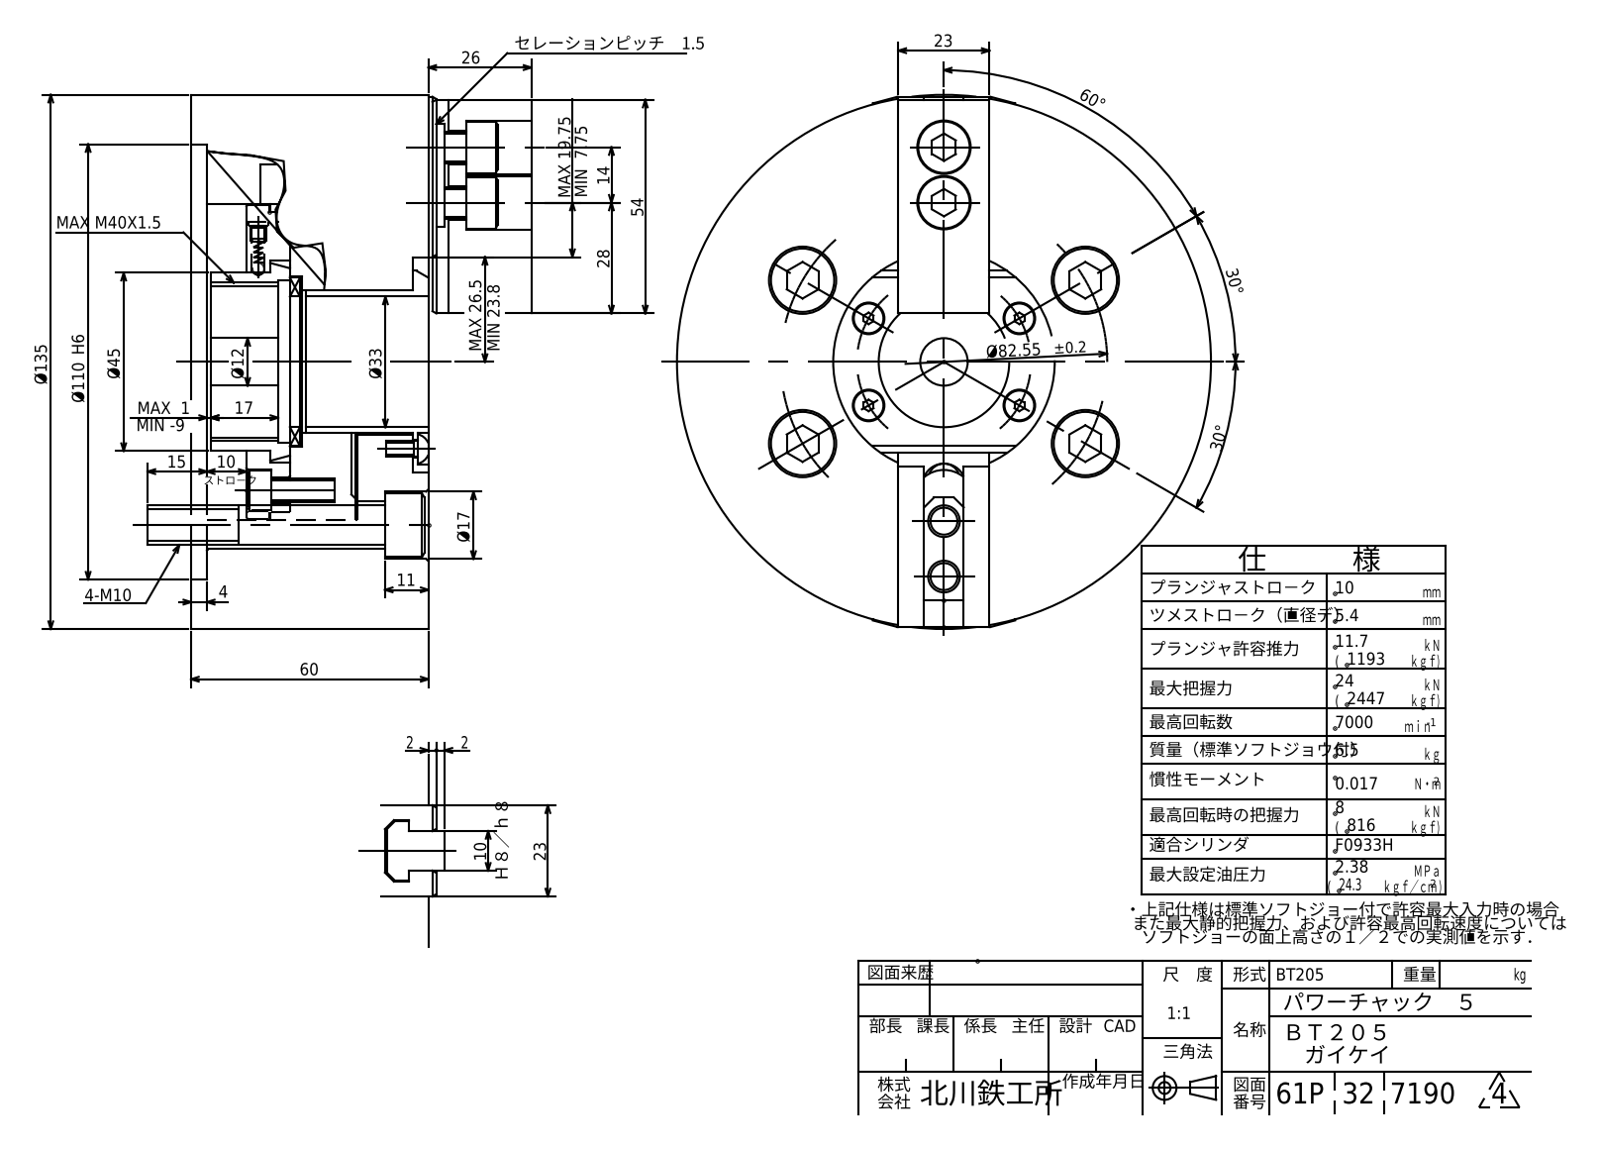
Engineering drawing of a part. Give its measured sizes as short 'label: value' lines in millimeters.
written by: Unknown (AUTOMOTIVE_DESIGN)
unit: mm
bodies: 3 solids, 195 faces (106 planar, 28 cylindrical, 61 other)
size: 135 × 135 × 86
volume: 631 446 mm³; area: 84 408 mm²
holes: 4× ⌀3.24, 4× ⌀8.5, 4× ⌀11, 4× ⌀13.5, 4× ⌀17, 1× ⌀37, 1× ⌀56, 1× ⌀80, 1× ⌀110
bosses: 1× ⌀135
face distances: 4, 56, 60, 42, 38, 18, 23, 61, 1, 57
hole spacings: 22, 41, 19, 34.28, 35.54, 40.27, 46.57, 48.48
